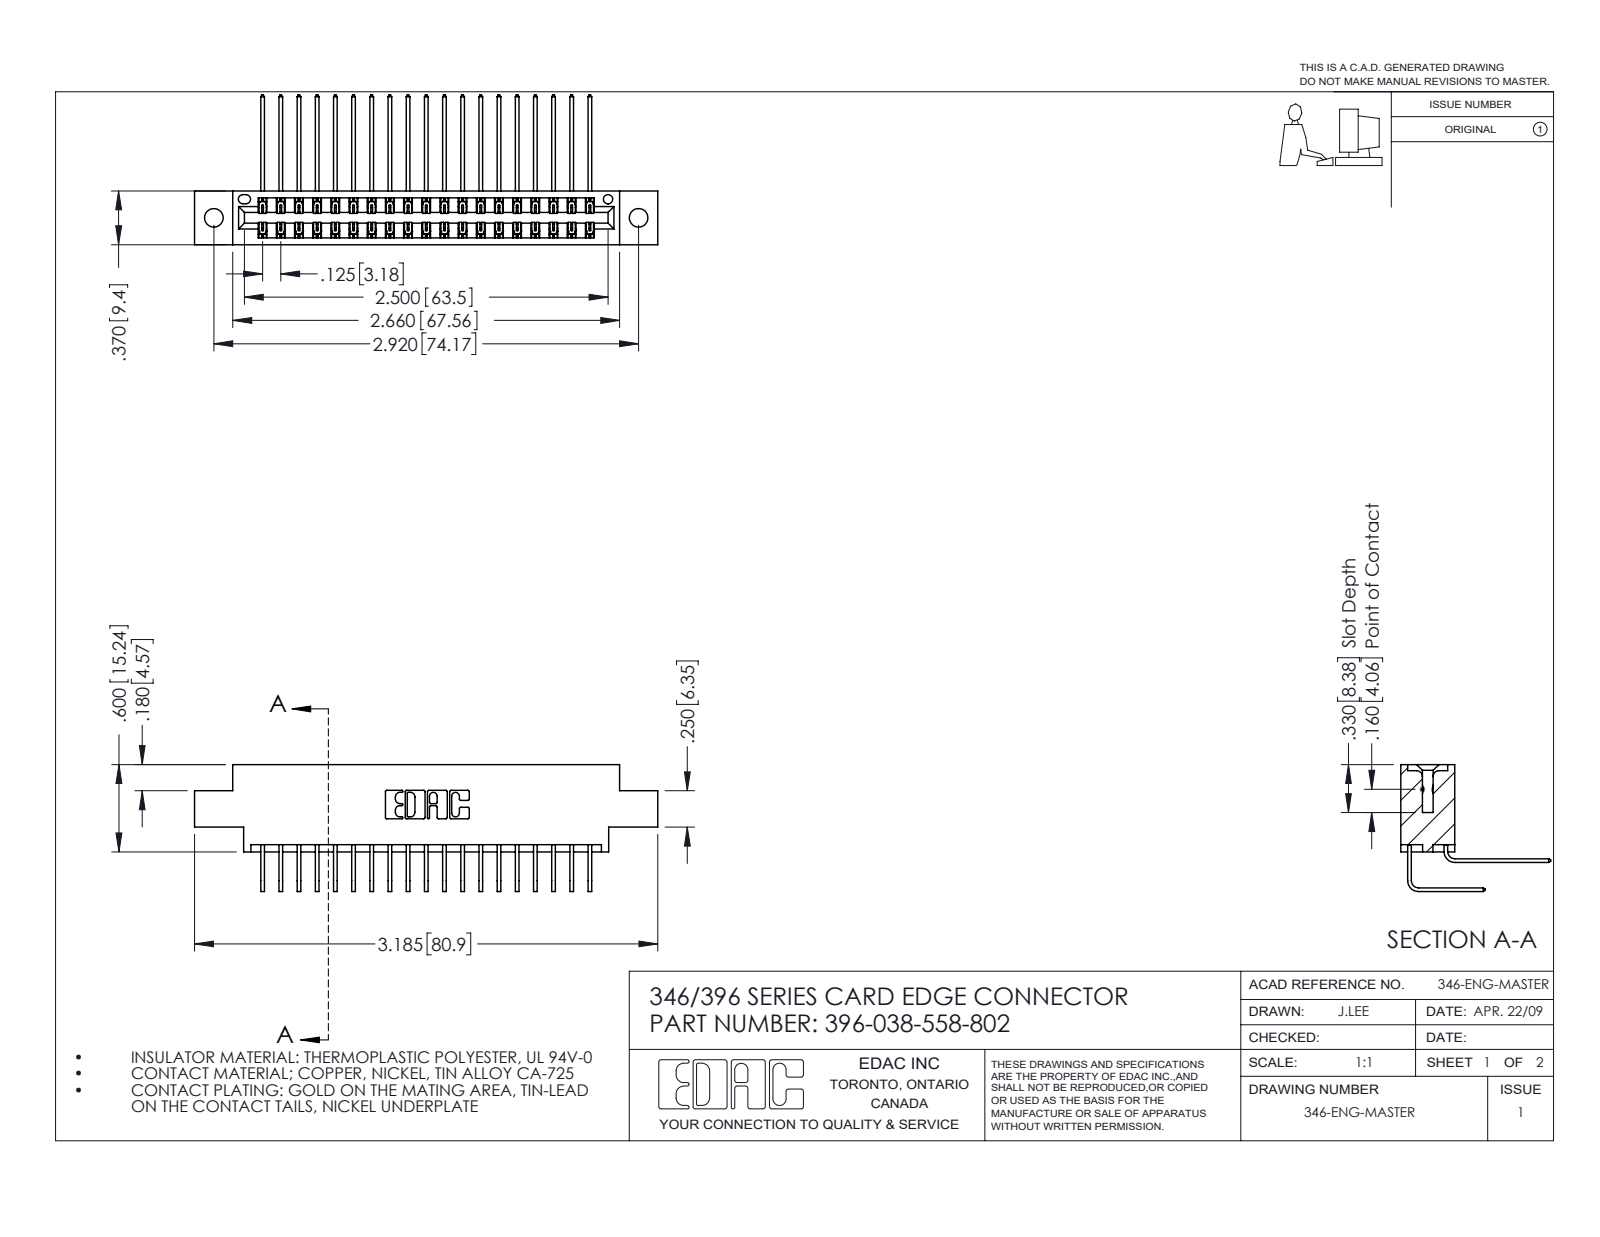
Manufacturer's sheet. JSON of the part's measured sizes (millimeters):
{"part_name": "345-292-001_558 Tail - 2; 346 Part_0.170 Offset - 0.128 Dia; 396-038-558-802; 345-292-001_558 559 Tail - 1", "step_written_by": "SolidWorks 2016 (CONFIG_CONTROL_DESIGN)", "units": "millimeters", "bodies": {"solids": 39, "faces": 2178, "planar": 1486, "cylindrical": 692, "other": 0}, "overall_size": [80.9, 26.2, 22.2], "volume_mm3": 7730, "surface_area_mm2": 11240, "round_holes": [[3.3, 2], [1.6, 1]], "partial_cylinders_radius": [[0.2, 57], [0.3, 22], [0.2, 6], [0.8, 6], [0.7, 3], [0.4, 2], [0.6, 2], [0.6, 2]], "face_to_face_distances": [8.2, 1.2, 9.4, 6.4, 0.6, 7.6, 1.8, 7, 3.8, 5.6], "hole_center_spacings": [6.2, 68.9, 74.2]}
